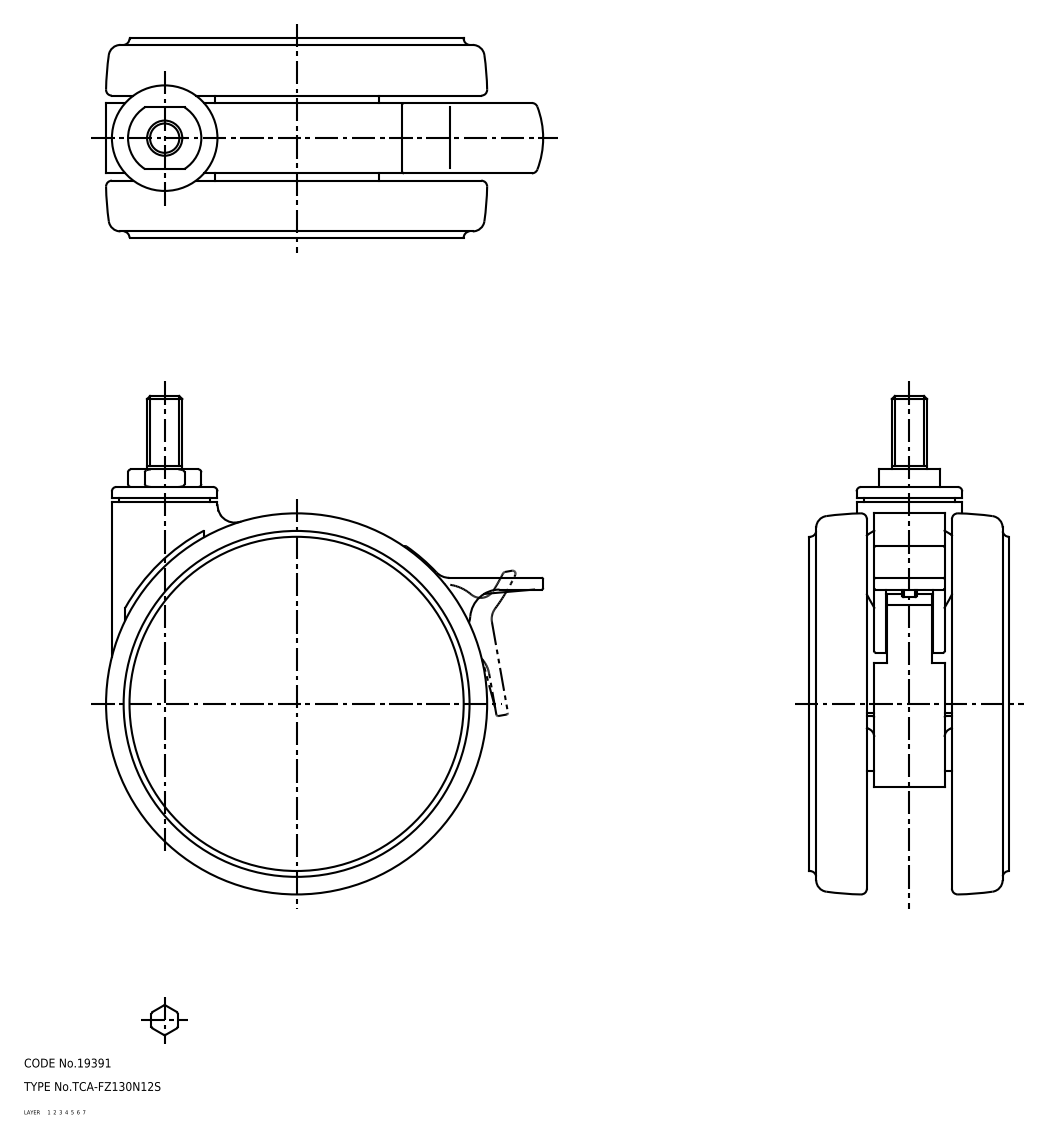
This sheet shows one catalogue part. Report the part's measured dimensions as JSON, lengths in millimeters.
{"part_name": "caster; TCA-FZ130N12S", "step_written_by": "SolidWorks 2015 (AUTOMOTIVE_DESIGN)", "units": "millimeters", "bodies": {"solids": 1, "faces": 2579, "planar": 767, "cylindrical": 1112, "other": 700}, "overall_size": [170, 149.11, 68.2], "volume_mm3": 514062, "surface_area_mm2": 192871, "round_holes": [[3, 2], [3.25, 2], [1.8, 1], [3.2, 1], [9.1, 1], [10, 1], [10.1, 1], [10.5, 1], [11.5, 1], [12, 1], [15, 1], [15.2, 1]], "round_bosses_or_shafts": [[117.8, 1], [114, 1], [42, 1], [36, 1], [31, 1], [27.9, 1], [27.6, 1], [20, 1]], "partial_cylinders_radius": [[0.5, 126], [1.5, 110], [1, 74], [0.3, 44], [2, 19], [0.2, 16], [3, 9], [4, 5]], "face_to_face_distances": [2, 66.2, 1.8, 3.8, 62.4, 64.4, 11.3, 7.5, 56.9, 9.3], "hole_center_spacings": [31.24, 39.66, 57.03]}
